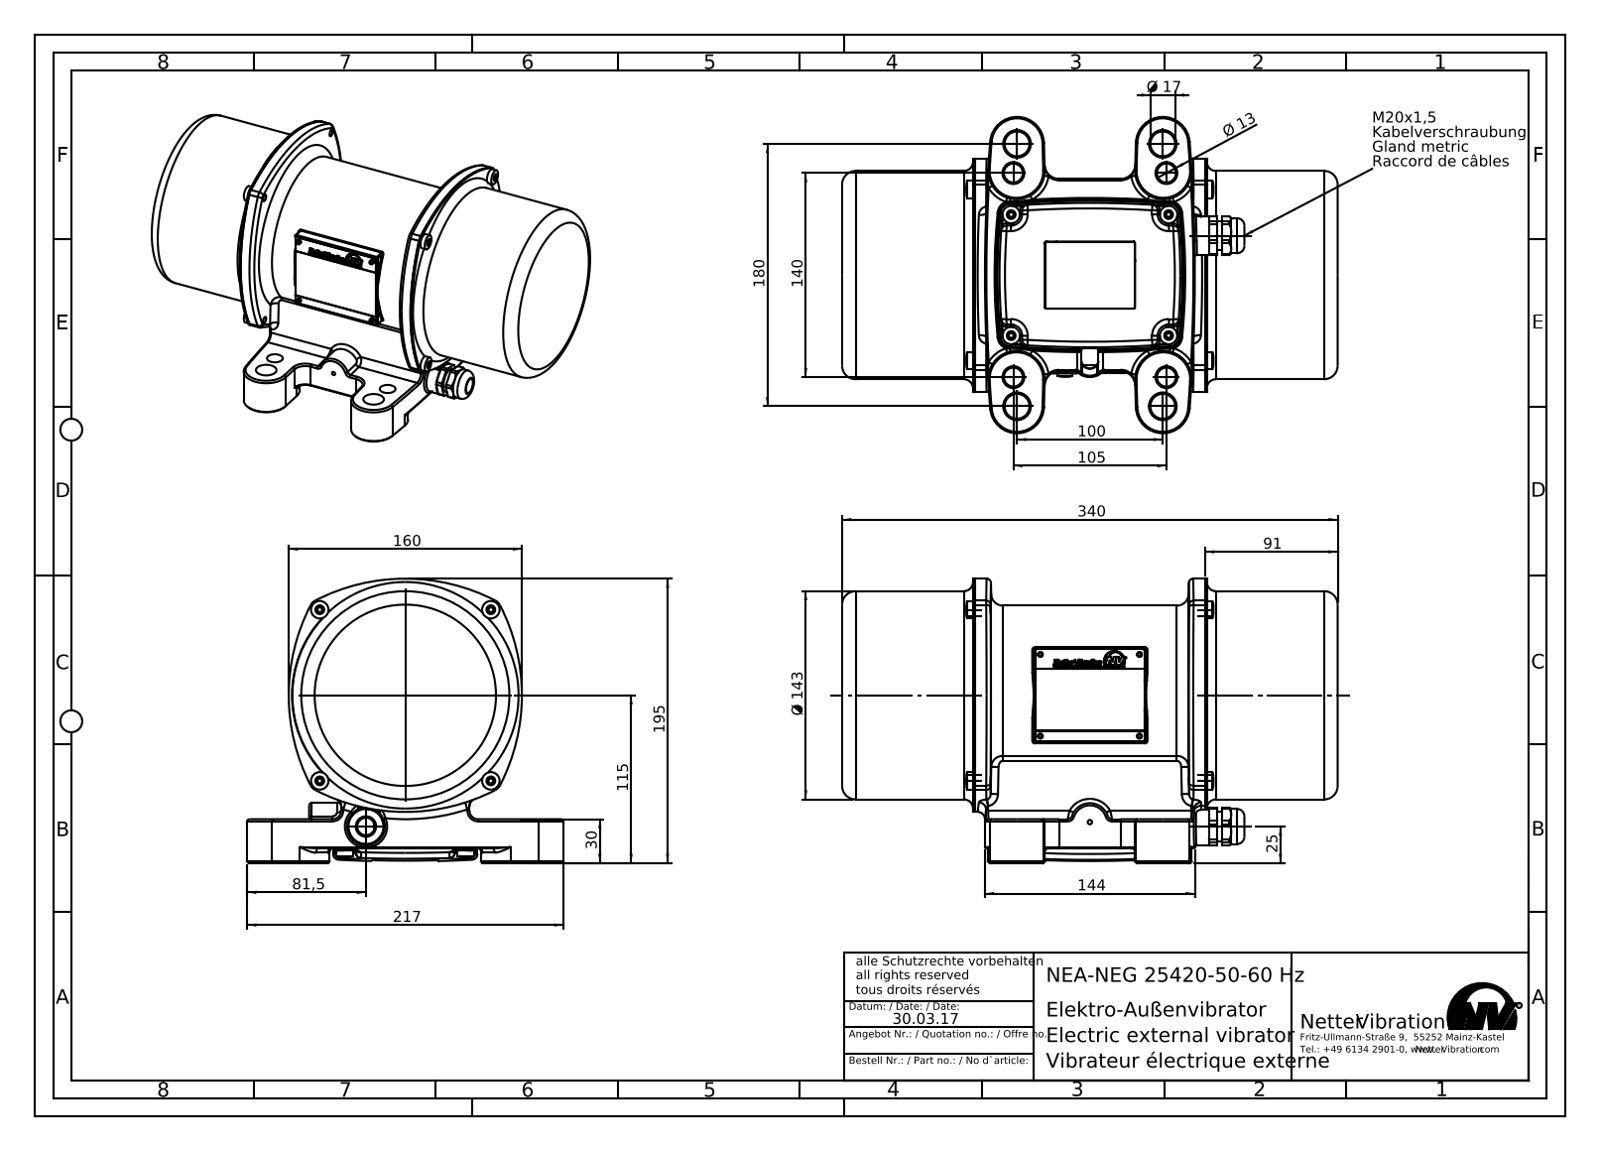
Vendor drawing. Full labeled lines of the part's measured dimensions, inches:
Part name (STEP PRODUCT): NEA-NEG 25420-50-60 Hz
STEP written by: SolidWorks 2015 (AUTOMOTIVE_DESIGN)
Units: inches
Bodies: 22 solids, 2440 faces (708 planar, 614 cylindrical, 1118 other)
Overall size (bounding box): 13.386 × 8.543 × 7.677
Volume: 83.18 in³ · Surface area: 882.6 in²
Round holes (diameter × count): ⌀0.134 ×4, ⌀0.256 ×4, ⌀0.276 ×4, ⌀0.512 ×4, ⌀0.669 ×4, ⌀0.472 ×2, ⌀0.551 ×2, ⌀0.571 ×1, ⌀0.728 ×1, ⌀4.803 ×1, ⌀5.528 ×1
Round bosses / shafts (diameter × count): ⌀0.472 ×8, ⌀0.236 ×8, ⌀0.276 ×2, ⌀5.622 ×1, ⌀0.945 ×1, ⌀0.787 ×1, ⌀0.63 ×1, ⌀0.394 ×1
Partial cylindrical surfaces — rounded edges, fillets, slot ends (radius × count): R0.079 ×56, R0.039 ×34, R0.02 ×33, R0.059 ×16, R0.118 ×14, R0.01 ×12, R0.069 ×9, R0.089 ×9
Main face-to-face distances: 0.047, 13.339, 3.535, 9.803, 0.591, 13.386, 13.291, 3.583, 9.756, 3.15
Hole centre spacings: 3.268, 0.794, 1.124, 1.916, 4.111, 4.341, 4.39, 4.518
